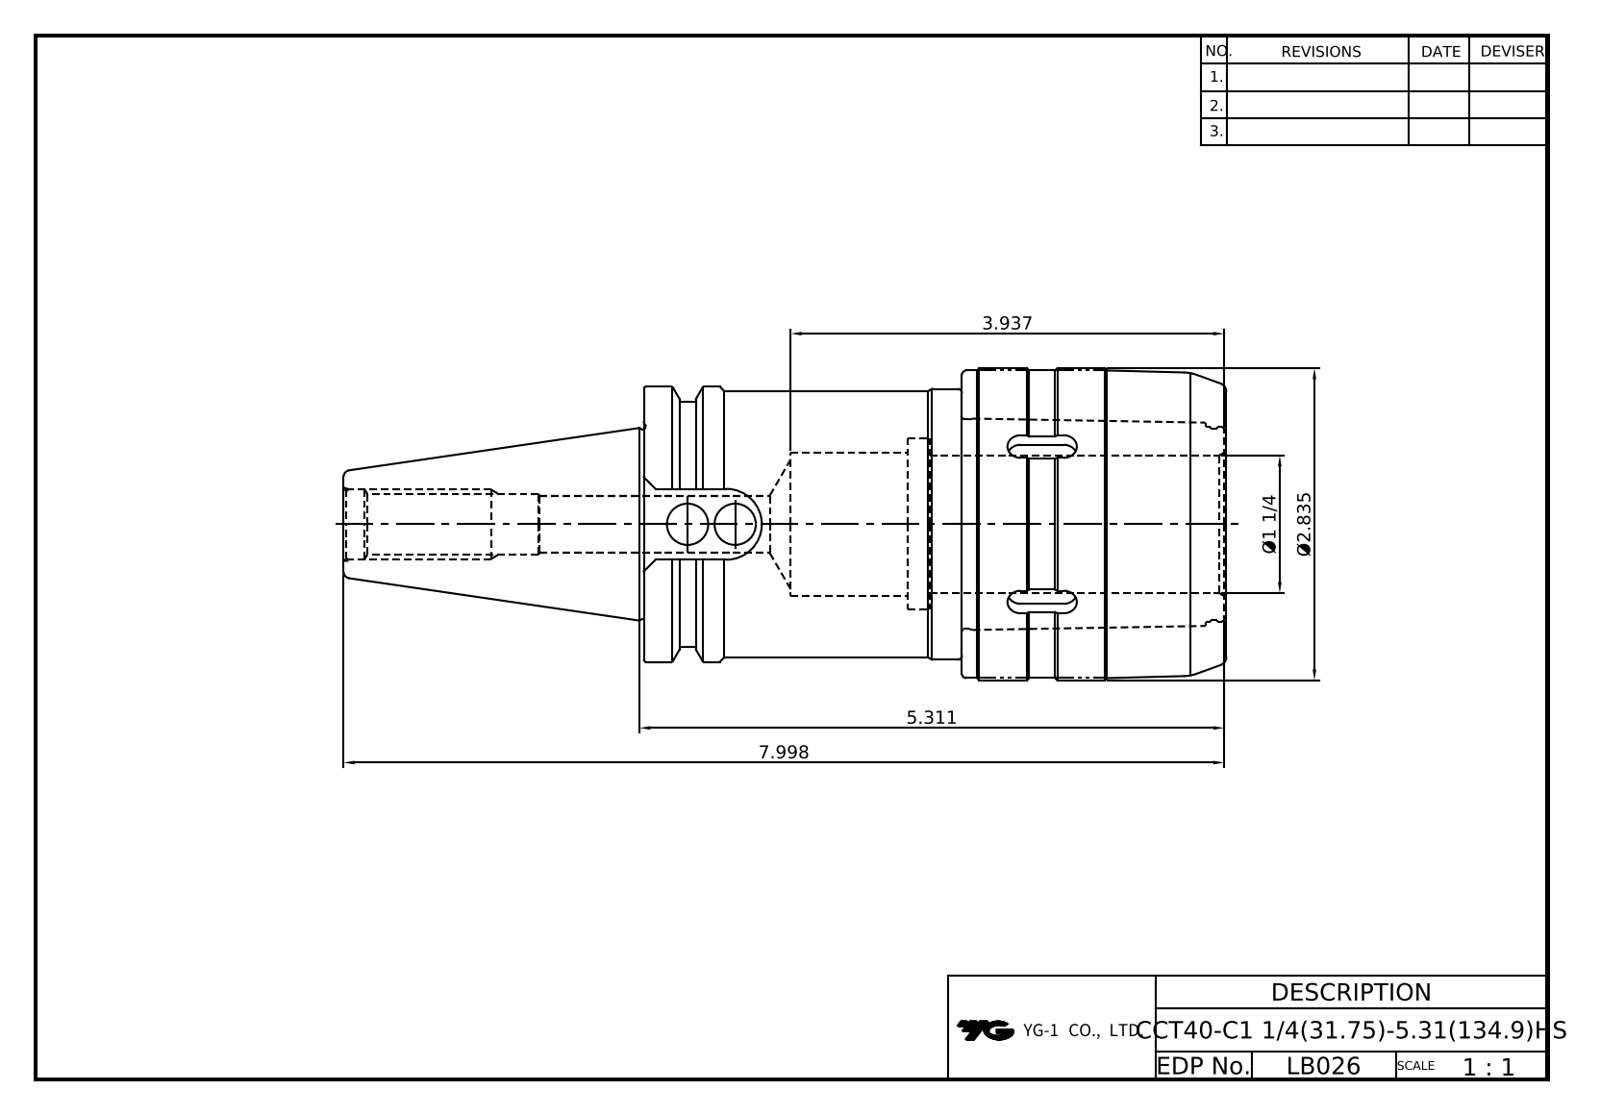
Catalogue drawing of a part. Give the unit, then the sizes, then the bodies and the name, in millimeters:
Units: millimetres
Overall size (bounding box): 203.75 × 72 × 72
Round holes (diameter × count): ⌀9.53 ×1, ⌀13 ×1, ⌀13.39 ×1, ⌀16.3 ×1, ⌀31.75 ×1, ⌀33 ×1, ⌀39.5 ×1, ⌀56 ×1, ⌀58 ×1
Round bosses / shafts (diameter × count): ⌀72 ×1, ⌀71 ×1, ⌀63.5 ×1, ⌀62.5 ×1, ⌀61.5 ×1, ⌀56.3 ×1, ⌀45 ×1, ⌀43.8 ×1
Partial cylindrical surfaces — rounded edges, fillets, slot ends (radius × count): R3 ×12, R8.19 ×1
Main face-to-face distances: 73.5, 61, 134, 60.5, 134.5, 0.5, 34, 39.5, 100, 100.5
Volume: 397 671 mm³ · Surface area: 80 548 mm²
Bodies: 2 solids, 176 faces (77 planar, 45 cylindrical, 54 other)
Part name (STEP PRODUCT): CCT40-C31.75-135HS; C32-CAP
STEP written by: Autodesk Inventor 2022 (AUTOMOTIVE_DESIGN)
